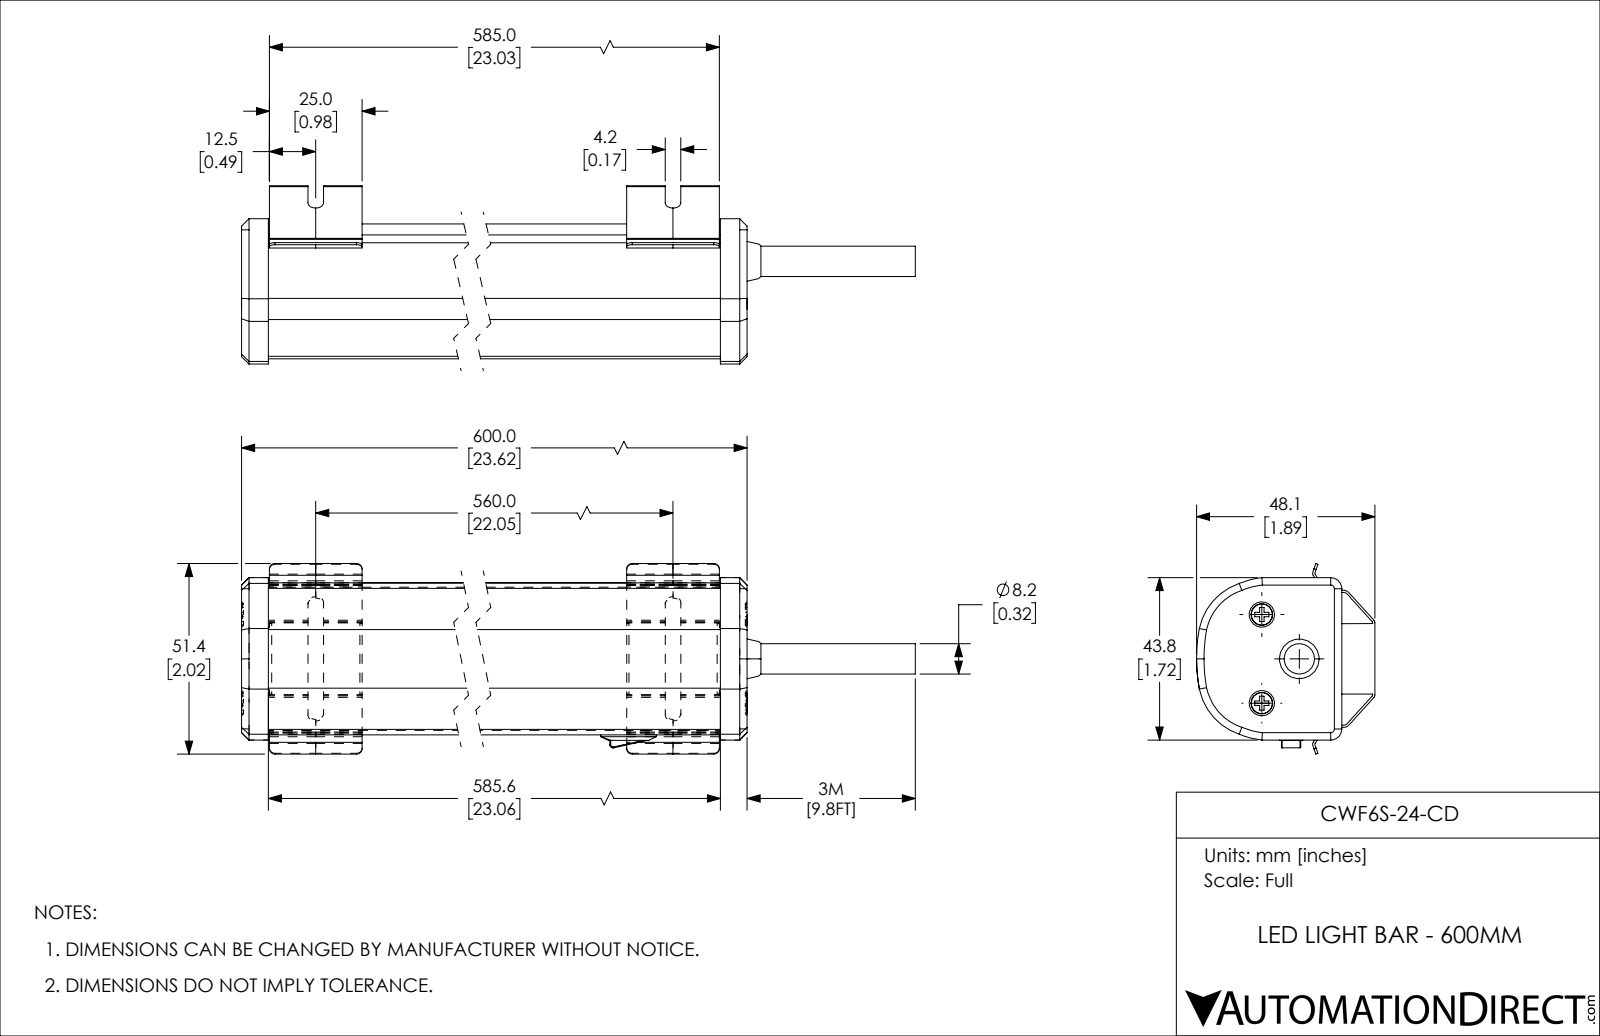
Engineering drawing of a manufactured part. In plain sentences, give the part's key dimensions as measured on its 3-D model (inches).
The part is named "CWF6S-24-CD". Its 3-D file was written by "SolidWorks 2018 (AUTOMOTIVE_DESIGN)". It is 3 solids with 283 faces: 123 planar, 67 cylindrical and 93 other. Overall it measures 25.409 by 2.023 by 1.894 inches. Its volume is 50 cubic inches and its surface area 153.3 square inches. Round bosses or shafts: 2 of diameter 0.224, 1 of diameter 0.323. Partial cylindrical surfaces (rounded edges, fillets, slot ends): 8 of radius 0.059, 4 of radius 0.083, 2 of radius 0.006, 2 of radius 0.008, 2 of radius 0.016, 2 of radius 0.03, 2 of radius 0.039, 2 of radius 0.591. The main face-to-face distances are 1.614, 0.047, 1.567, 0.024, 0.083, 1.52, 23.622, 22.047, 0.606, 0.523.
